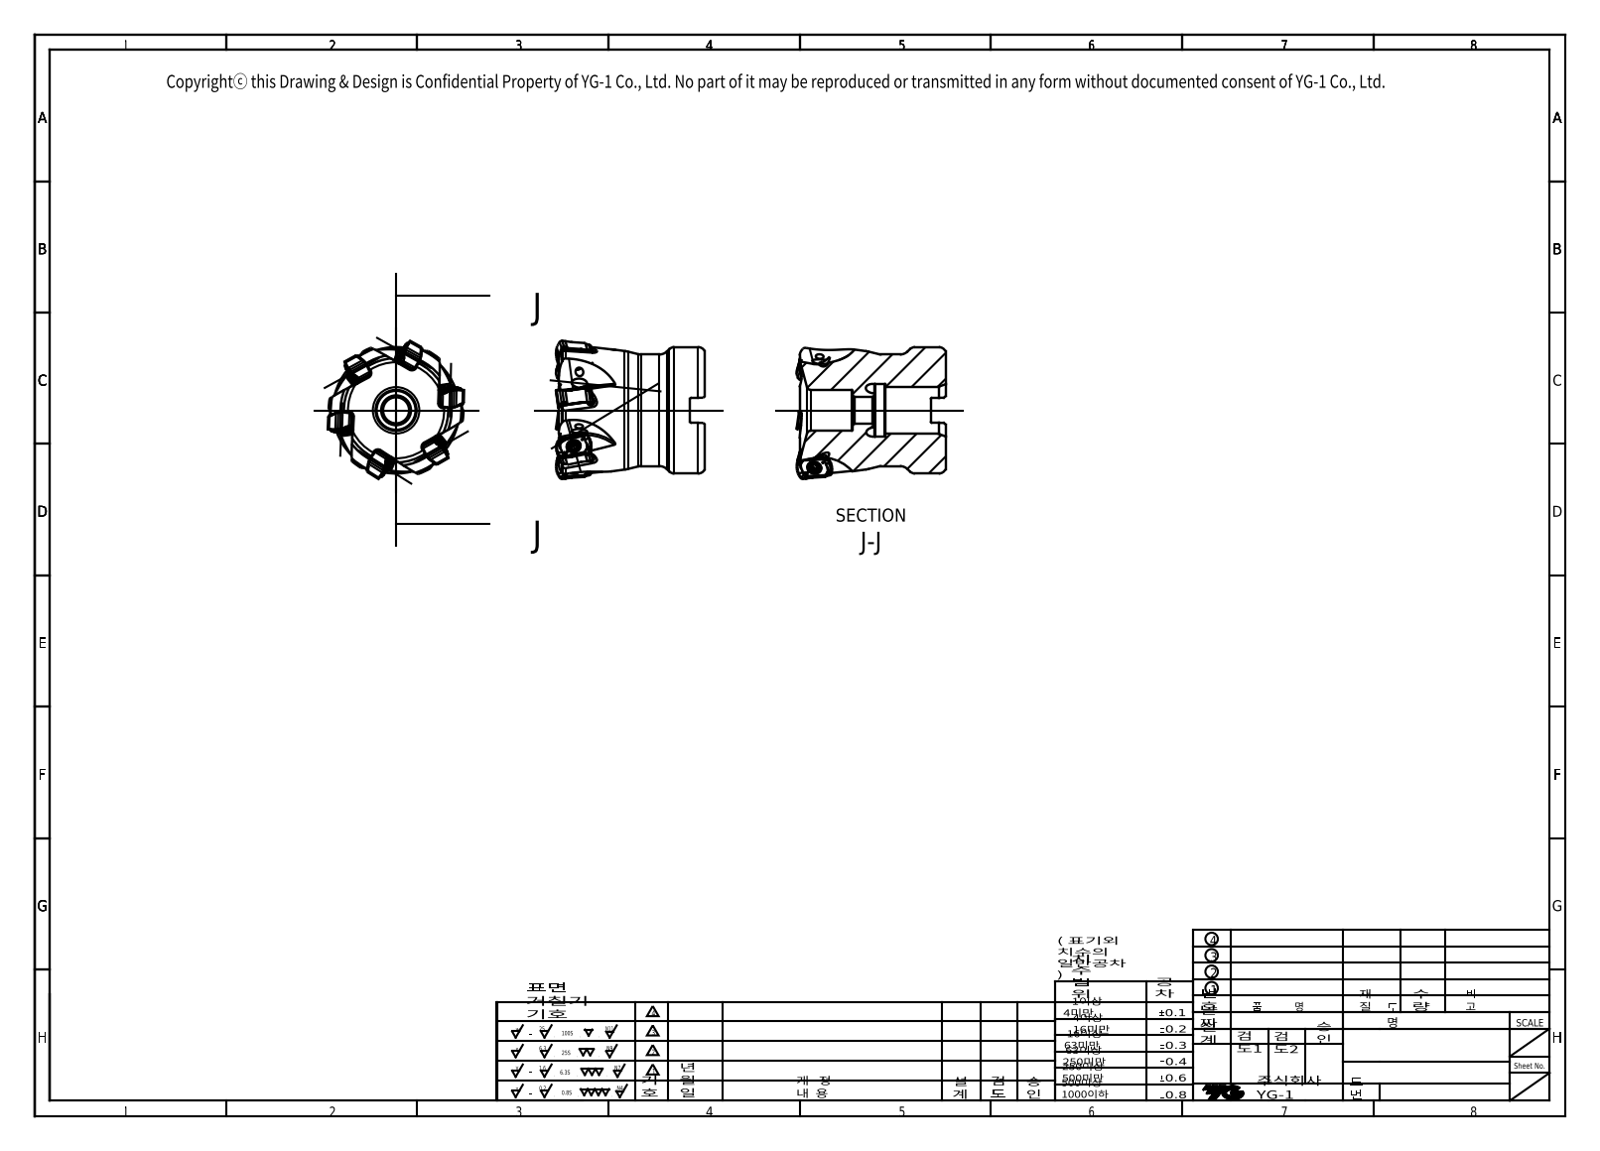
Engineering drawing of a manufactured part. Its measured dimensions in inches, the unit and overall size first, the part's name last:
Units: inches
Overall size (bounding box): 1.575 × 1.501 × 1.501
Round holes (diameter × count): ⌀0.276 ×1, ⌀0.433 ×1, ⌀0.5 ×1, ⌀0.563 ×1
Round bosses / shafts (diameter × count): ⌀1.339 ×1, ⌀1.181 ×1
Partial cylindrical surfaces — rounded edges, fillets, slot ends (radius × count): R0.016 ×2
Main face-to-face distances: 1.53, 1.374, 0.156, 0.78, 0.594, 0.75, 0.259, 0.521, 1.115, 1.271
Volume: 1.862 in³ · Surface area: 11.77 in²
Bodies: 1 solid, 83 faces (17 planar, 10 cylindrical, 56 other)
Part name (STEP PRODUCT): 12014C04DDBA1s2q
STEP written by: SIEMENS PLM Software NX 10.0 (AP203_CONFIGURATION_CONTROLLED_3D_DESIGN_OF_MECHANICAL_PARTS_AND_ASSEMBLIES_MIM_LF)
